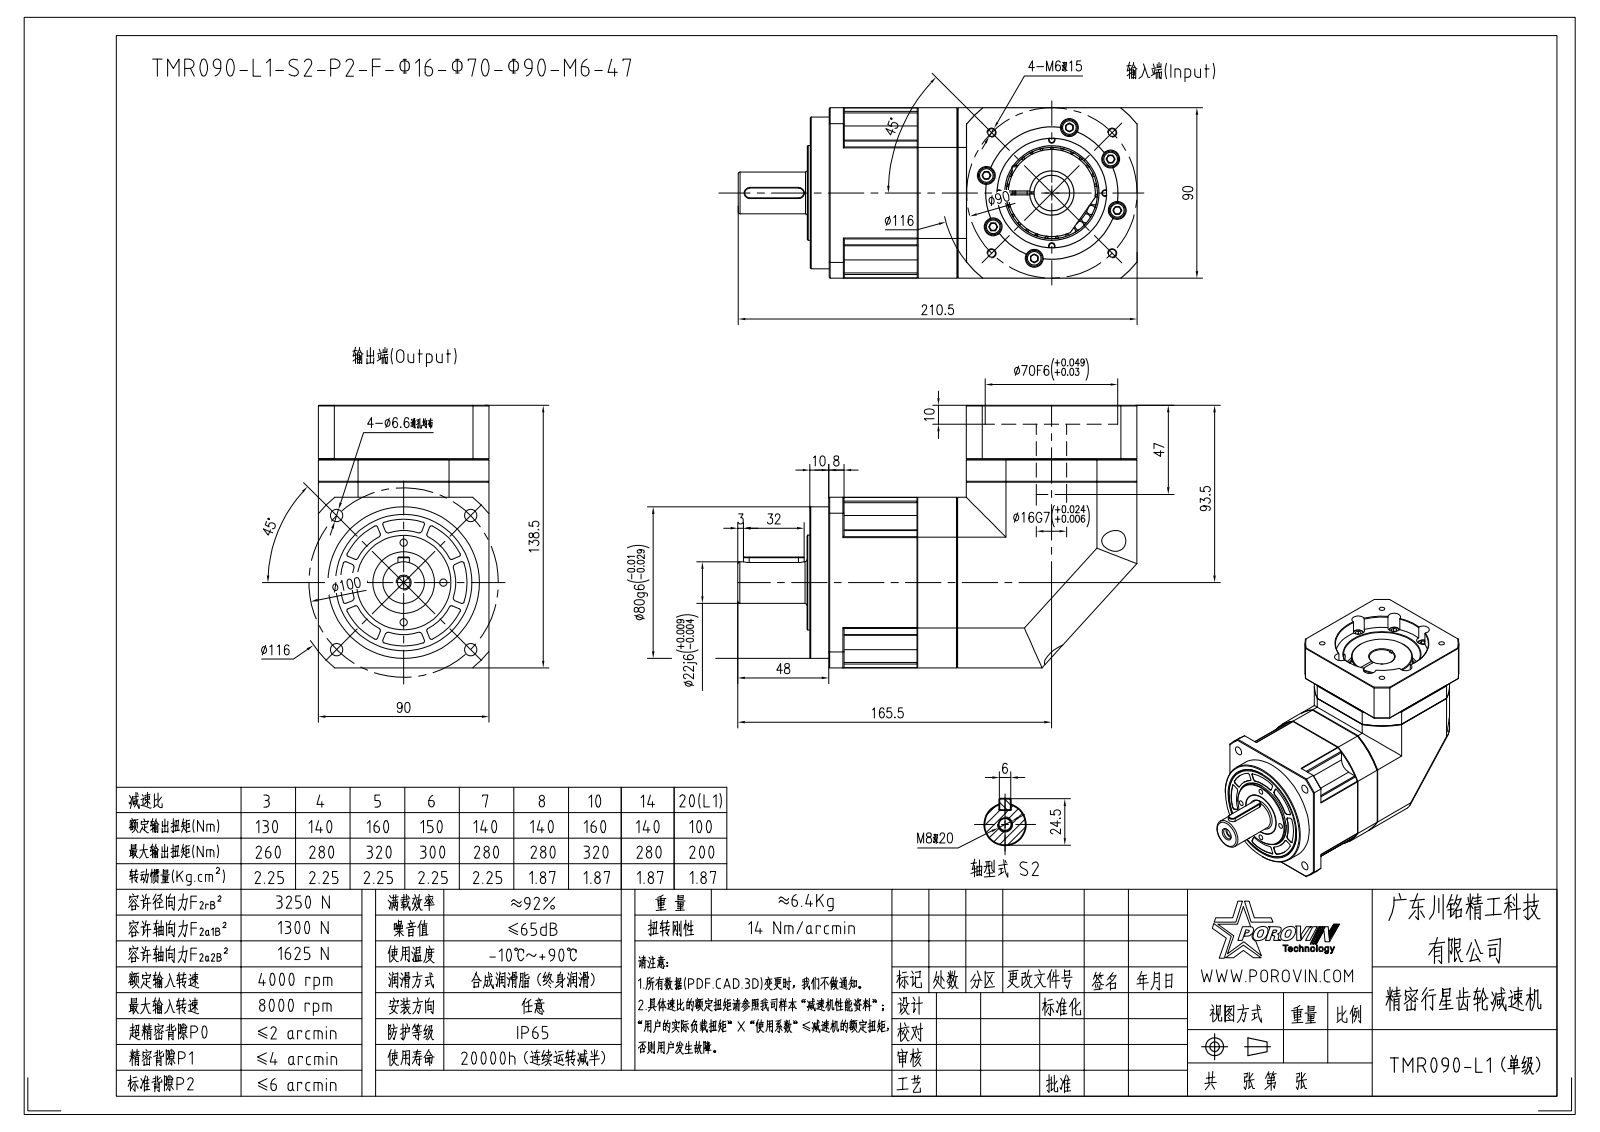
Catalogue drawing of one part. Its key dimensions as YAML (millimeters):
part_name: "HEXAGON_SOCKET_HEAD_CAP_S-13622; SPRING_LOCK_WASHERS--NORM-24193; SPRING_LOCK_WASHERS--NORMA-2869; HEXAGON_SOCKET_HEAD_CAP_SC-2921 (+8 more)"
step_written_by: "CREO PARAMETRIC BY PTC INC, 2020053 (CONFIG_CONTROL_DESIGN)"
units: millimeters
bodies: {solids: 43, faces: 1295, planar: 516, cylindrical: 548, other: 231}
overall_size: [210.5, 138.5, 90]
volume: 1342000
surface_area: 210129
round_holes:
  - {diameter: 5.4, count: 12}
  - {diameter: 5.5, count: 12}
  - {diameter: 9.5, count: 12}
  - {diameter: 4.2, count: 7}
  - {diameter: 5, count: 5}
  - {diameter: 6.5, count: 5}
  - {diameter: 4, count: 4}
  - {diameter: 6.6, count: 4}
  - {diameter: 6.68, count: 4}
  - {diameter: 11, count: 4}
  - {diameter: 6.8, count: 1}
  - {diameter: 8.4, count: 1}
round_bosses_or_shafts:
  - {diameter: 8.5, count: 12}
  - {diameter: 8, count: 12}
  - {diameter: 5, count: 12}
  - {diameter: 10, count: 4}
  - {diameter: 9.88, count: 4}
  - {diameter: 6, count: 4}
  - {diameter: 80, count: 1}
  - {diameter: 78, count: 1}
partial_cylinders:
  - {radius: 1, count: 92}
  - {radius: 7.5, count: 4}
  - {radius: 51, count: 3}
  - {radius: 3, count: 2}
  - {radius: 58, count: 2}
  - {radius: 4, count: 1}
  - {radius: 5.25, count: 1}
  - {radius: 20.75, count: 1}
face_to_face_distances: [90, 12, 21.3, 21.5, 10, 26, 28.5, 110, 98, 31.3]
hole_center_spacings: [35.75, 27.36, 38.16, 66.06, 66.53, 64.31, 80.07, 13.97]
